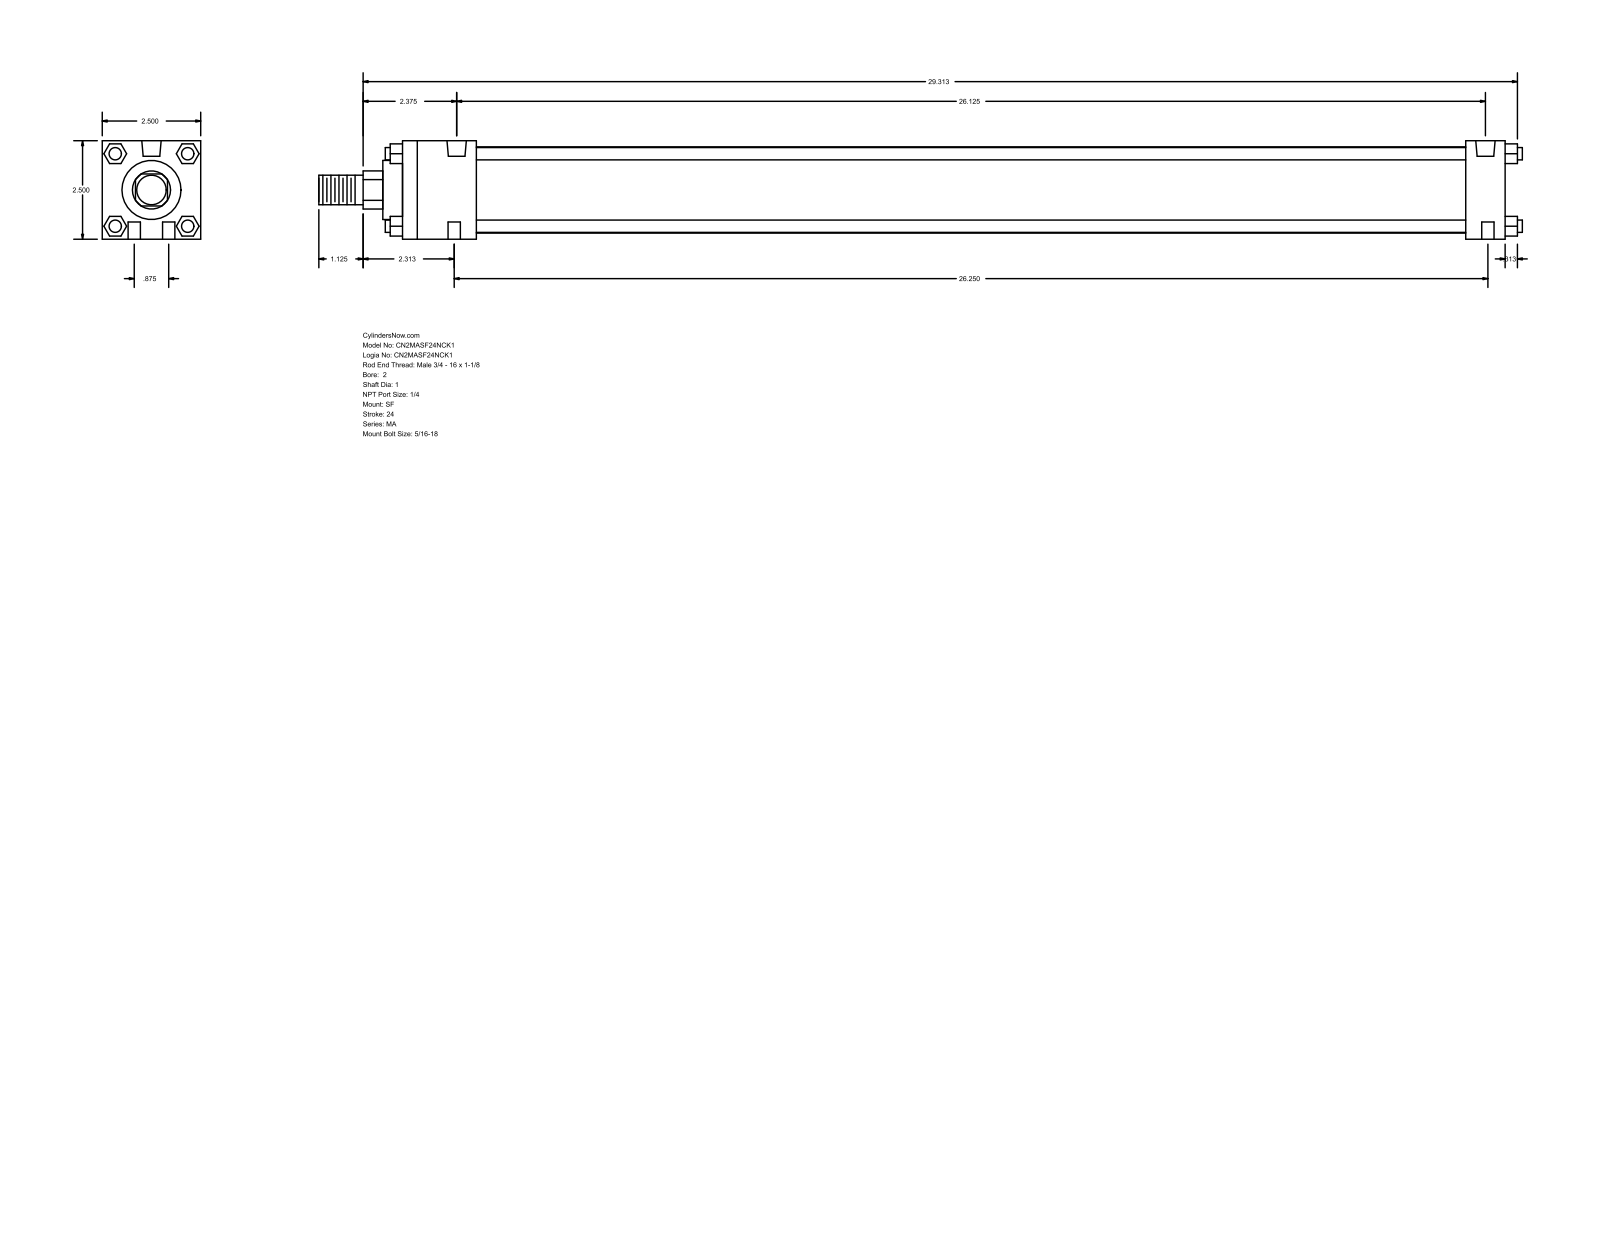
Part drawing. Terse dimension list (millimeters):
name: MA_SF__0200_1
written by: GSSL Pune (CONFIG_CONTROL_DESIGN)
unit: mm
bodies: 0 solids, 124 faces (94 planar, 30 cylindrical, 0 other)
size: 776.29 × 63.5 × 63.5
holes: 6× ⌀7.94, 2× ⌀12.49
bosses: 4× ⌀7.94, 1× ⌀55.63, 1× ⌀38.1, 1× ⌀25.4, 1× ⌀19.05
rounds: 1× R12.29
face distances: 63.5, 711.2, 12.7, 25.4, 685.8, 47.63, 638.17, 663.57, 23.37, 40.47
hole spacings: 11.22, 665.25, 22.22, 663.57, 666.75, 667.12
